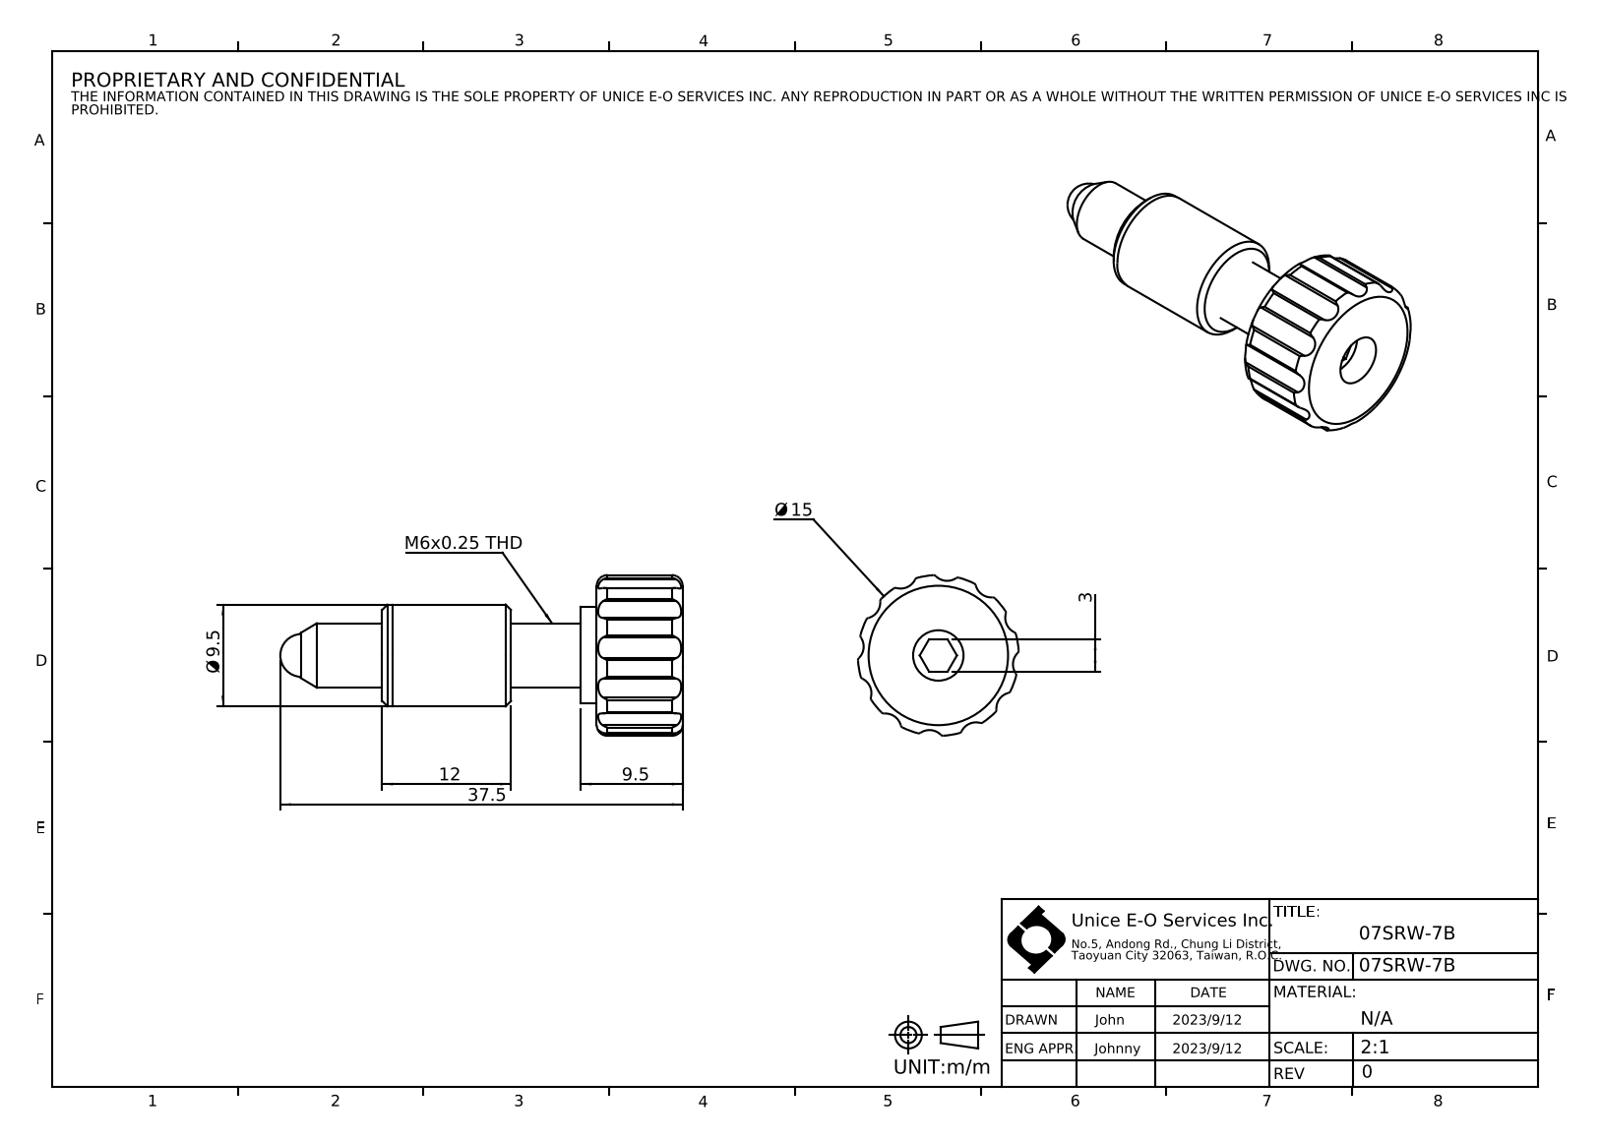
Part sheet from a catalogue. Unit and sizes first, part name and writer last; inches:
Units: inches
Overall size (bounding box): 1.476 × 0.589 × 0.589
Round holes (diameter × count): ⌀0.157 ×1, ⌀0.185 ×1, ⌀0.226 ×1, ⌀0.232 ×1
Round bosses / shafts (diameter × count): ⌀0.374 ×1, ⌀0.372 ×1, ⌀0.354 ×1, ⌀0.236 ×1
Partial cylindrical surfaces — rounded edges, fillets, slot ends (radius × count): R0.012 ×24, R0.059 ×12, R0.295 ×1
Main face-to-face distances: 0.315, 0.098, 0.217, 0.059, 0.374, 0.256, 0.63, 0.472, 0.728, 0.787
Volume: 0.161 in³ · Surface area: 3.545 in²
Bodies: 4 solids, 79 faces (16 planar, 56 cylindrical, 7 other)
Part name (STEP PRODUCT): 07SRW-7B
STEP written by: SolidWorks 2022 (CONFIG_CONTROL_DESIGN)
